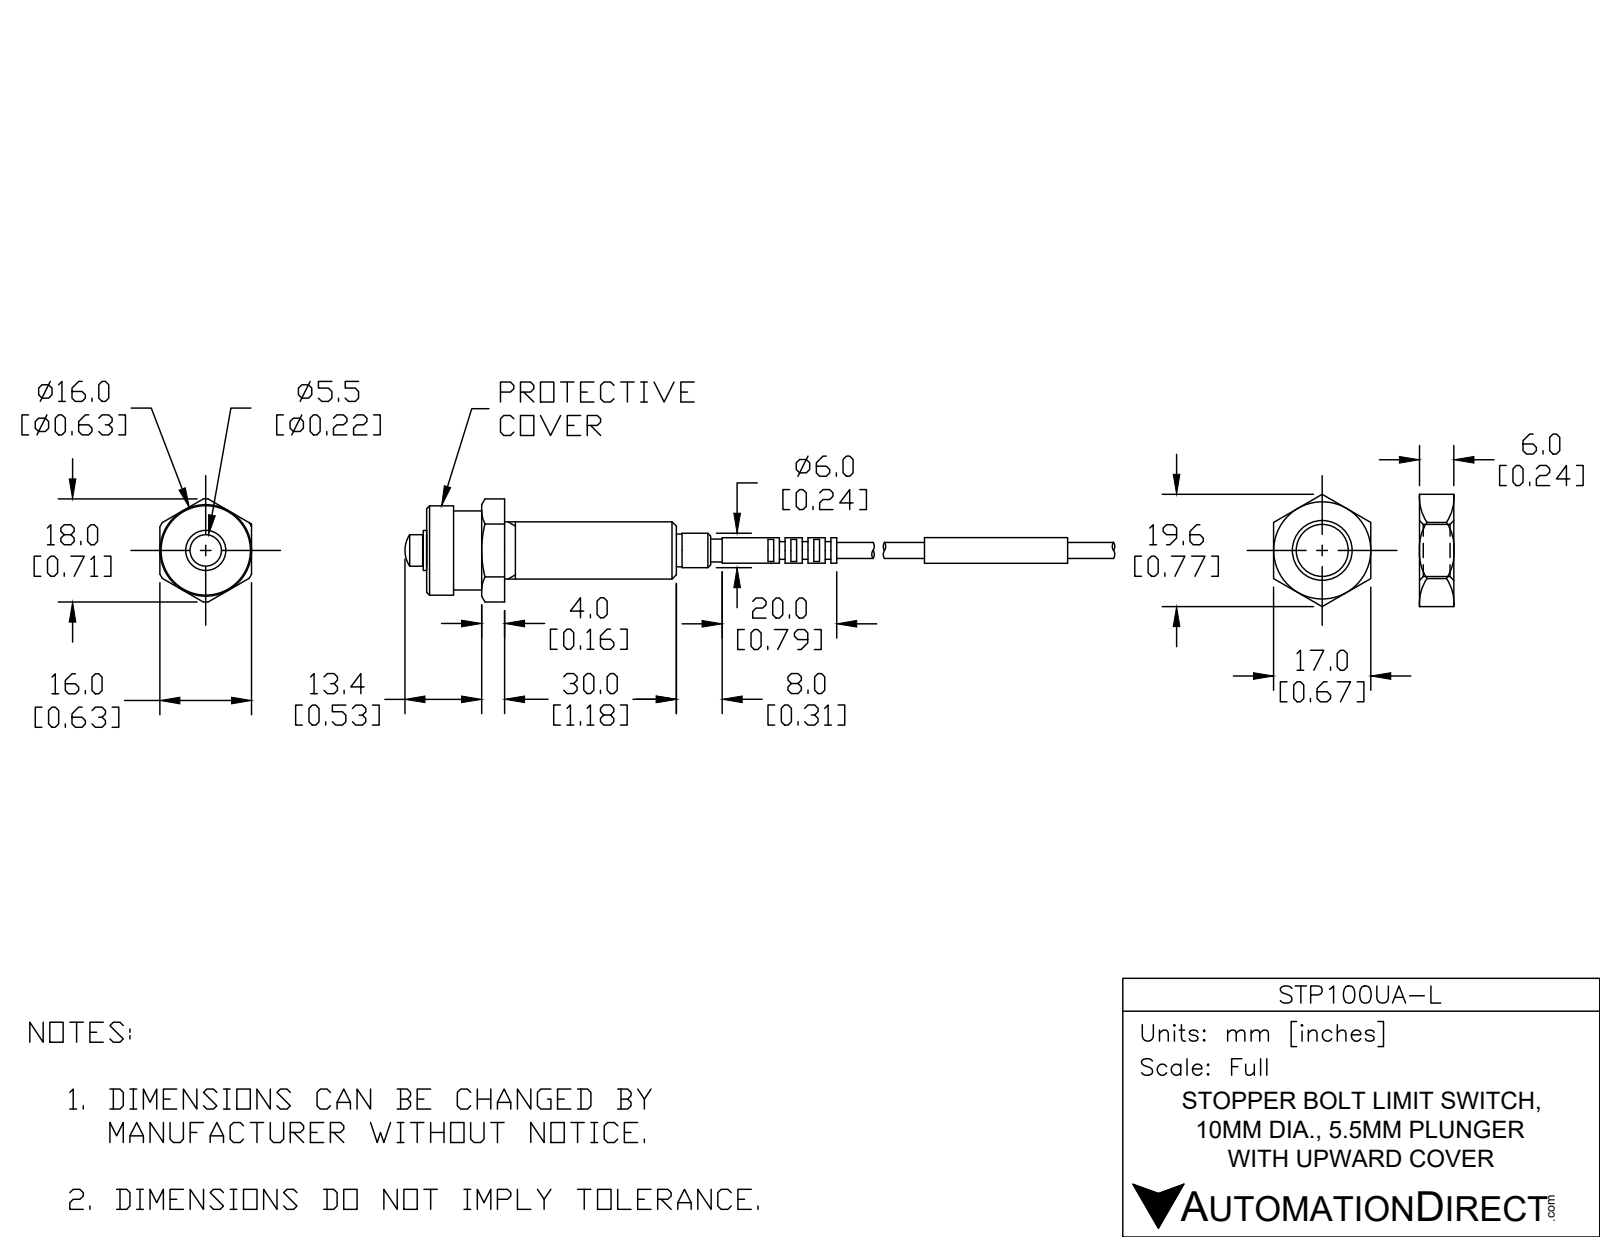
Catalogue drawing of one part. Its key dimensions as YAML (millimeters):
part_name: "STP100UA-L"
step_written_by: "SolidWorks 2017 (CONFIG_CONTROL_DESIGN)"
units: millimeters
bodies: {solids: 2, faces: 180, planar: 71, cylindrical: 87, other: 22}
overall_size: [126.4, 18, 16]
volume: 5571
surface_area: 3652
round_bosses_or_shafts:
  - {diameter: 15.6, count: 1}
  - {diameter: 13.8, count: 1}
  - {diameter: 10, count: 1}
  - {diameter: 6.99, count: 1}
  - {diameter: 6, count: 1}
  - {diameter: 5.7, count: 1}
  - {diameter: 5.5, count: 1}
  - {diameter: 4.9, count: 1}
partial_cylinders:
  - {radius: 9, count: 1}
face_to_face_distances: [13.6, 16, 4, 1, 3, 2, 9.6, 4.7, 4.9, 8.9]
